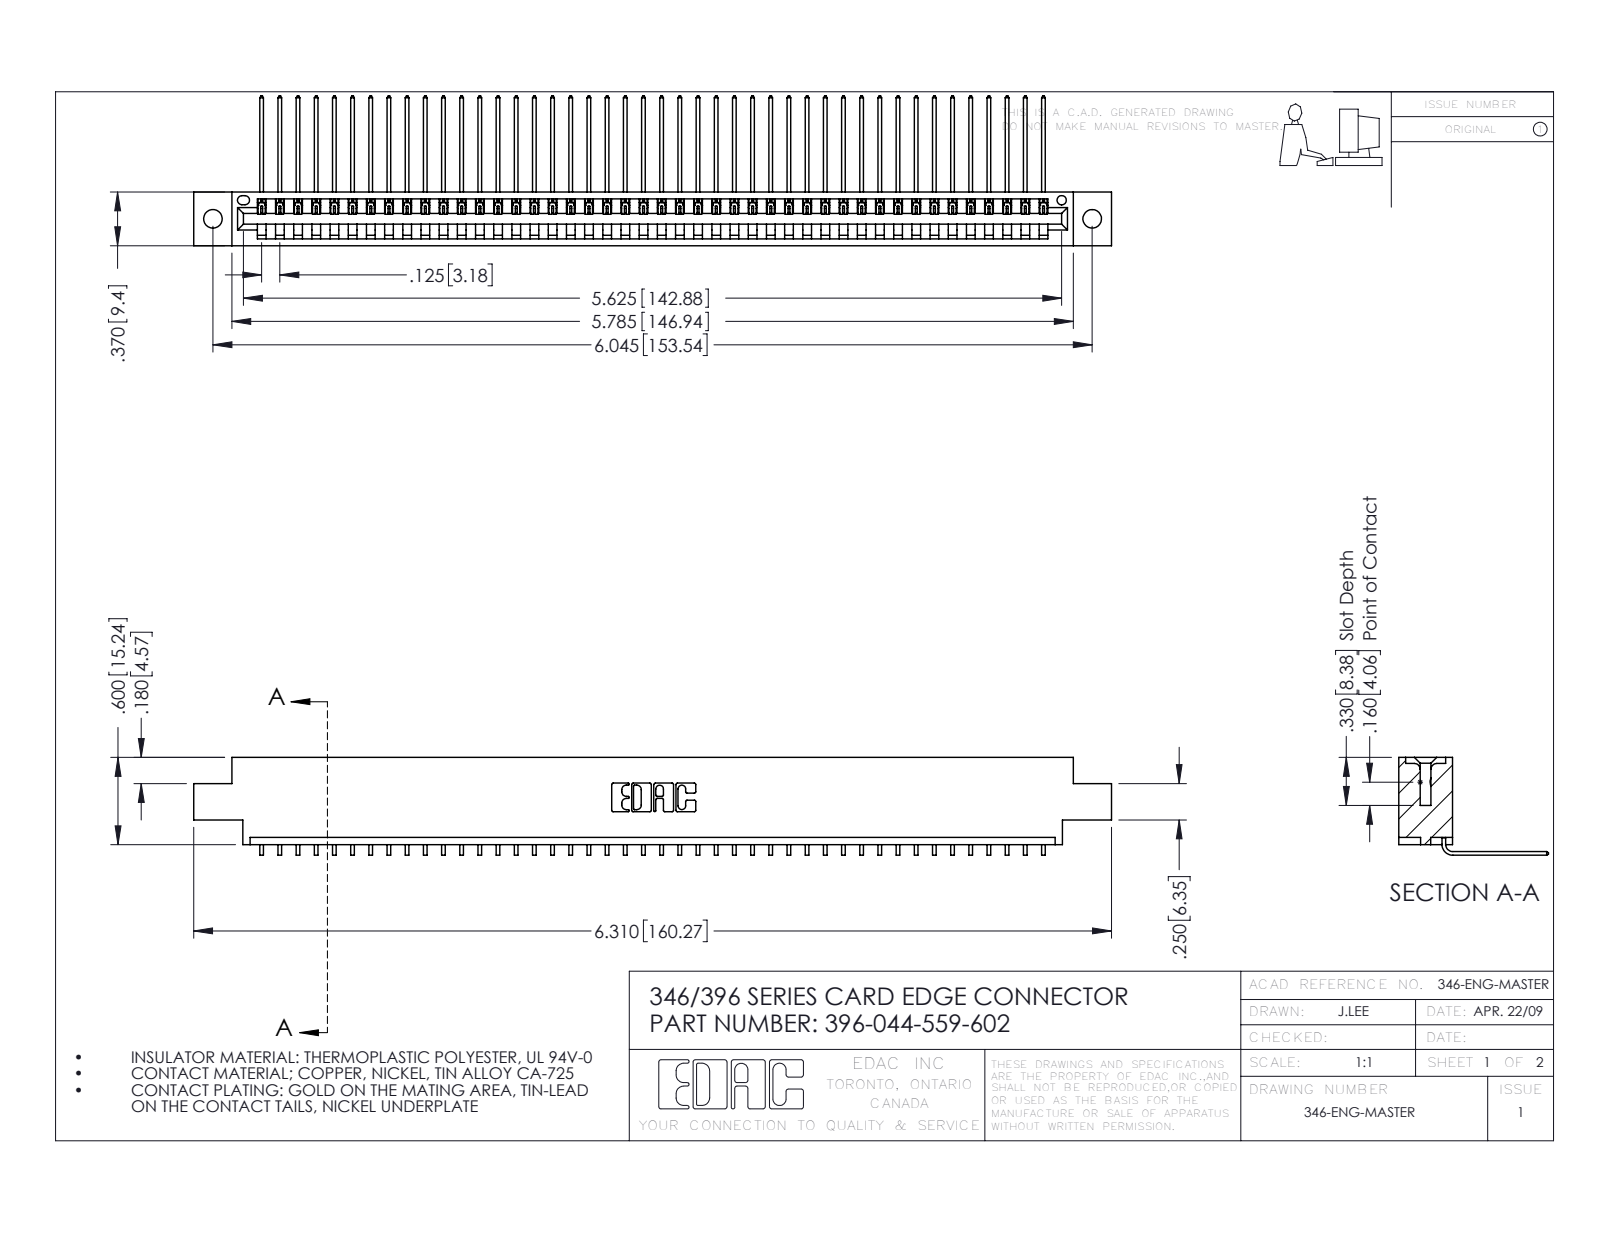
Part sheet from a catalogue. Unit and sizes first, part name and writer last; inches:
Units: inches
Overall size (bounding box): 6.31 × 1.03 × 0.673
Round holes (diameter × count): ⌀0.128 ×2, ⌀0.064 ×1
Partial cylindrical surfaces — rounded edges, fillets, slot ends (radius × count): R0.006 ×88, R0.01 ×22, R0.007 ×6, R0.031 ×6, R0.026 ×3, R0.031 ×2, R0.04 ×2, R0.014 ×1
Main face-to-face distances: 0.048, 0.322, 0.37, 0.025, 0.25, 0.072, 0.298, 0.148, 0.222, 0.1
Hole centre spacings: 0.246, 5.836, 6.045
Volume: 0.934 in³ · Surface area: 30.88 in²
Bodies: 45 solids, 2766 faces (1928 planar, 838 cylindrical, 0 other)
Part name (STEP PRODUCT): 345-292-001_558 559 Tail - 1; 396-044-559-602; 346 Part_0.170 Offset - 0.128 Dia
STEP written by: SolidWorks 2016 (CONFIG_CONTROL_DESIGN)
